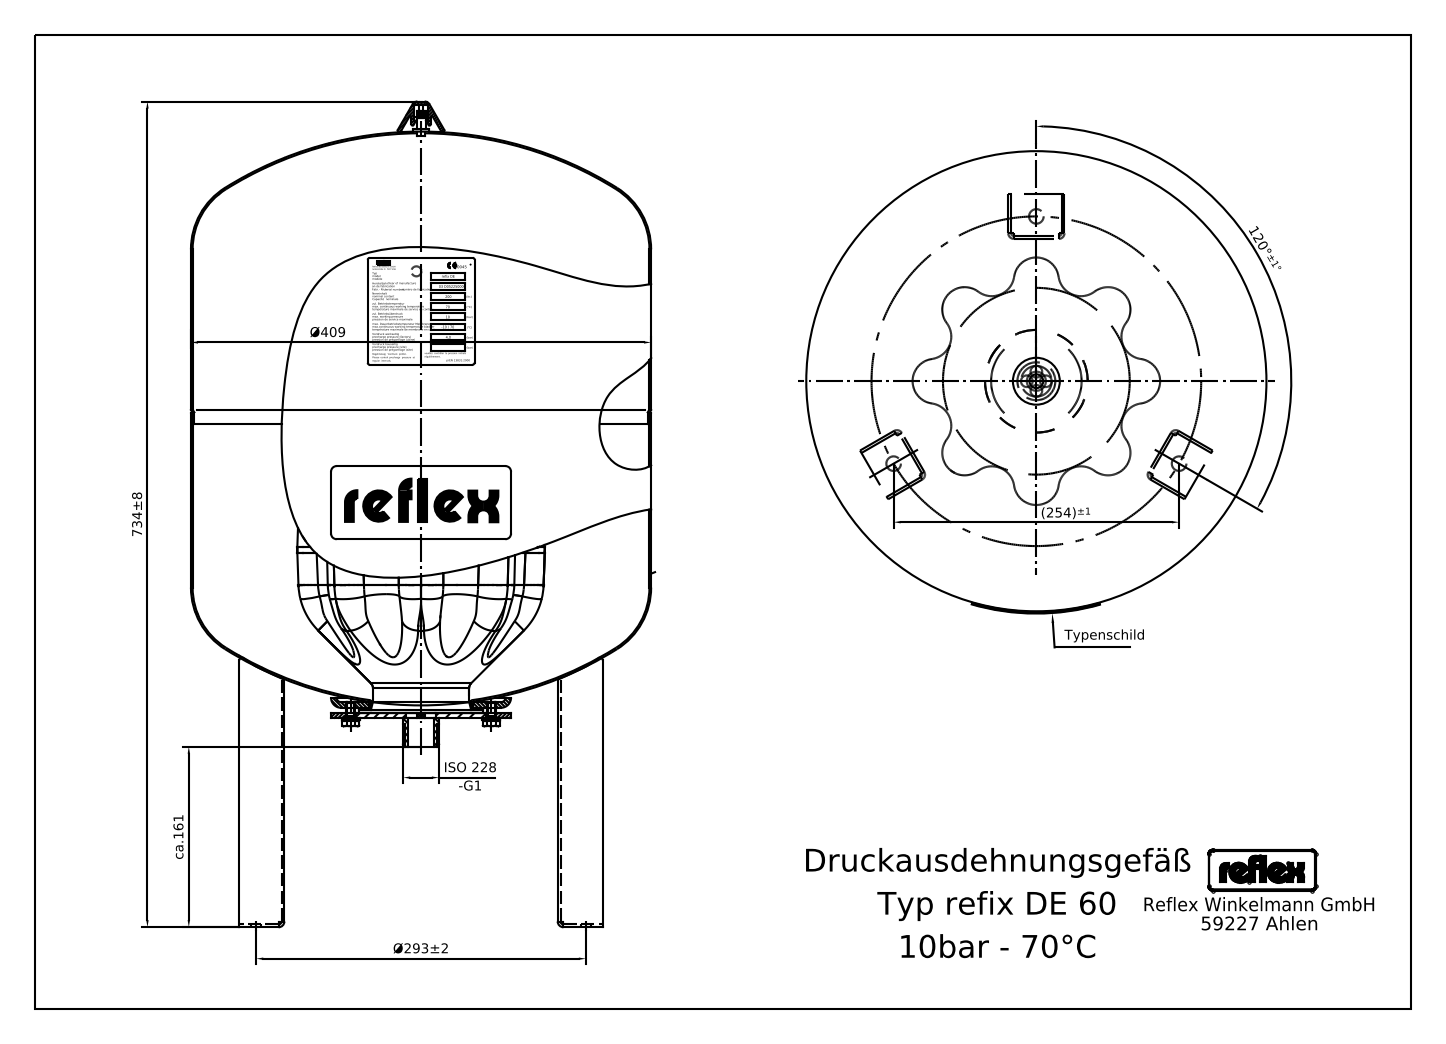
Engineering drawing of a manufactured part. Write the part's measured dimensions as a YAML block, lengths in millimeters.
step_written_by: "Mechanical Desktop 2009 (CONFIG_CONTROL_DESIGN)"
units: millimeters
bodies: {solids: 16, faces: 348, planar: 155, cylindrical: 125, other: 68}
overall_size: [737, 409, 409]
volume: 57120000
surface_area: 1589000
round_holes:
  - {diameter: 13.4, count: 3}
  - {diameter: 14.1, count: 1}
  - {diameter: 89, count: 1}
  - {diameter: 150, count: 1}
round_bosses_or_shafts:
  - {diameter: 8, count: 6}
  - {diameter: 409, count: 1}
  - {diameter: 160, count: 1}
  - {diameter: 140, count: 1}
  - {diameter: 33.7, count: 1}
  - {diameter: 17.1, count: 1}
  - {diameter: 9, count: 1}
  - {diameter: 6, count: 1}
partial_cylinders:
  - {radius: 1, count: 15}
  - {radius: 2.5, count: 15}
  - {radius: 5, count: 15}
  - {radius: 3.94, count: 4}
  - {radius: 1.57, count: 3}
  - {radius: 2.69, count: 2}
  - {radius: 4.72, count: 2}
  - {radius: 6.49, count: 2}
face_to_face_distances: [280, 2.5, 47.5, 5, 45, 50, 121, 401, 126, 406]
hole_center_spacings: [146.5, 253.74]
